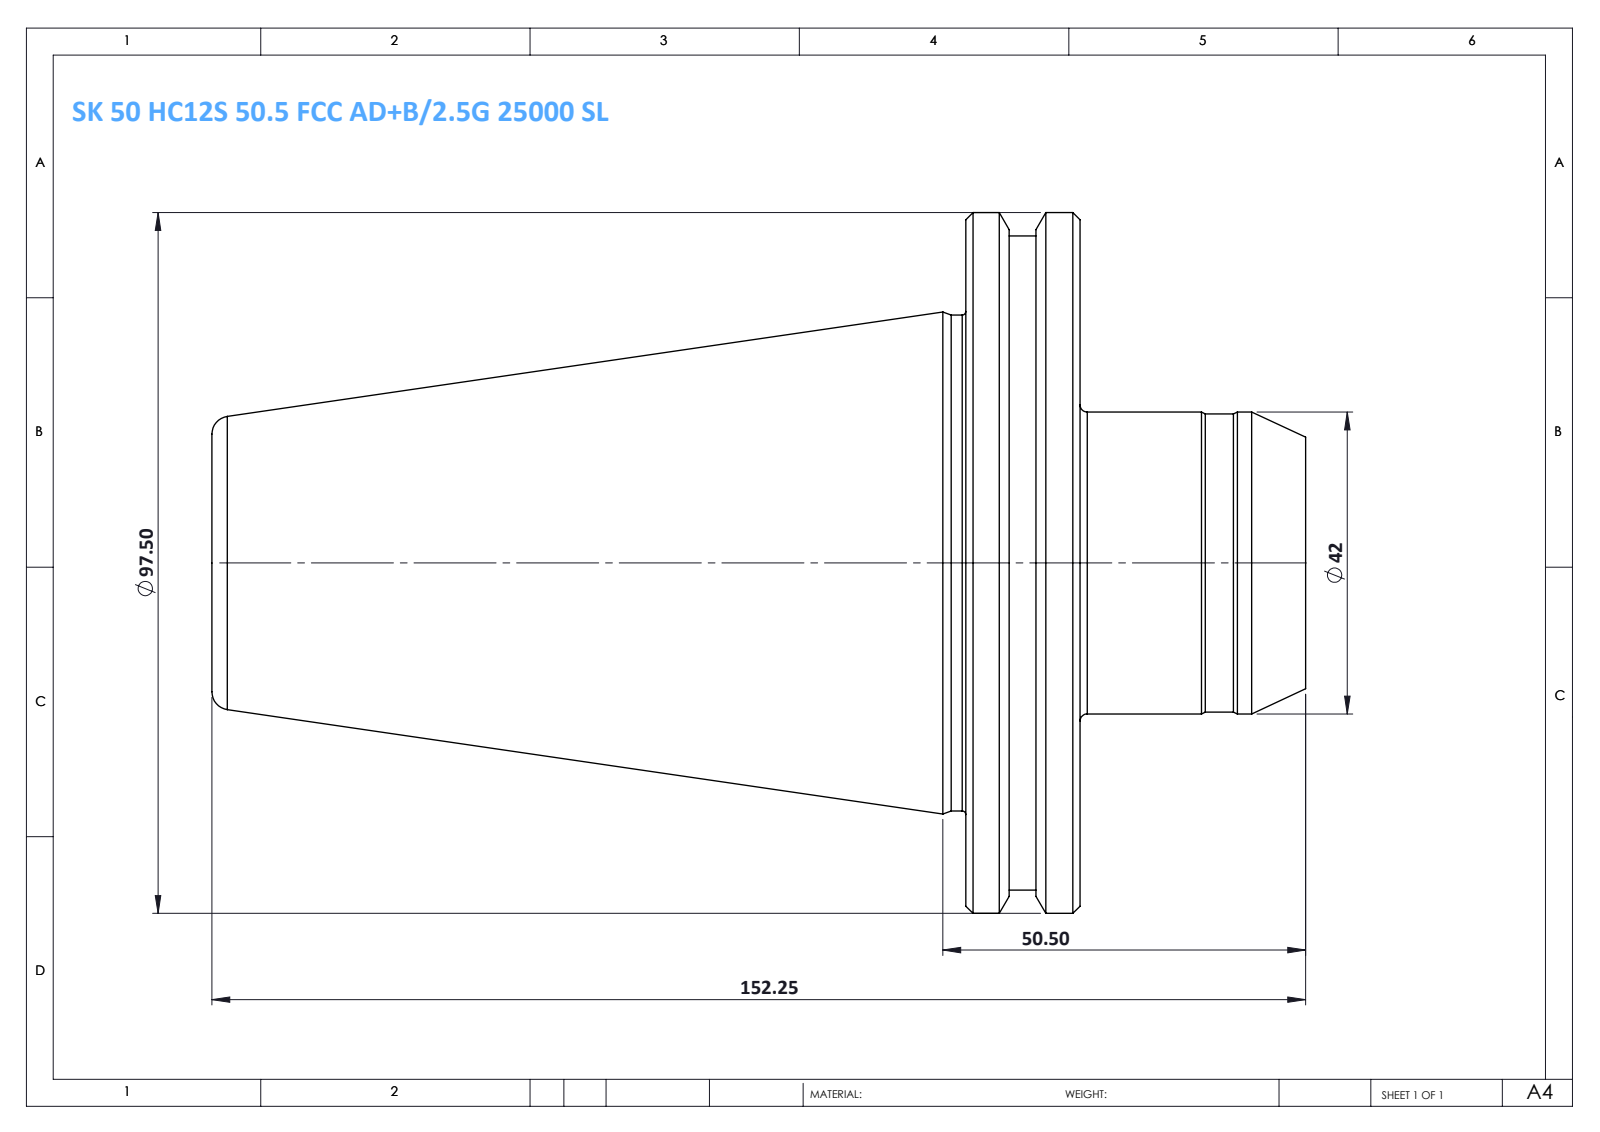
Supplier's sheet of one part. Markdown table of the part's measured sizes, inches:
| quantity | value |
| --- | --- |
| part name | SK 50 HC12S 50.5 FCC AD+B -2.5G 25000 SL |
| STEP written by | SolidWorks 2014 (CONFIG_CONTROL_DESIGN) |
| units | inches |
| bodies | 1 solid, 44 faces (6 planar, 14 cylindrical, 24 other) |
| overall size | 5.994 × 3.839 × 3.839 |
| volume | 25.34 in³ |
| surface area | 62.34 in² |
| round bosses / shafts (diameter × count) | 3.839 × 1, 3.583 × 1, 2.717 × 1, 1.654 × 1, 1.634 × 1 |
| main face-to-face distances | 0.626, 4.758, 4.132, 1.236, 1.862, 5.994, 1.478, 0.241, 0.385, 4.517 |
